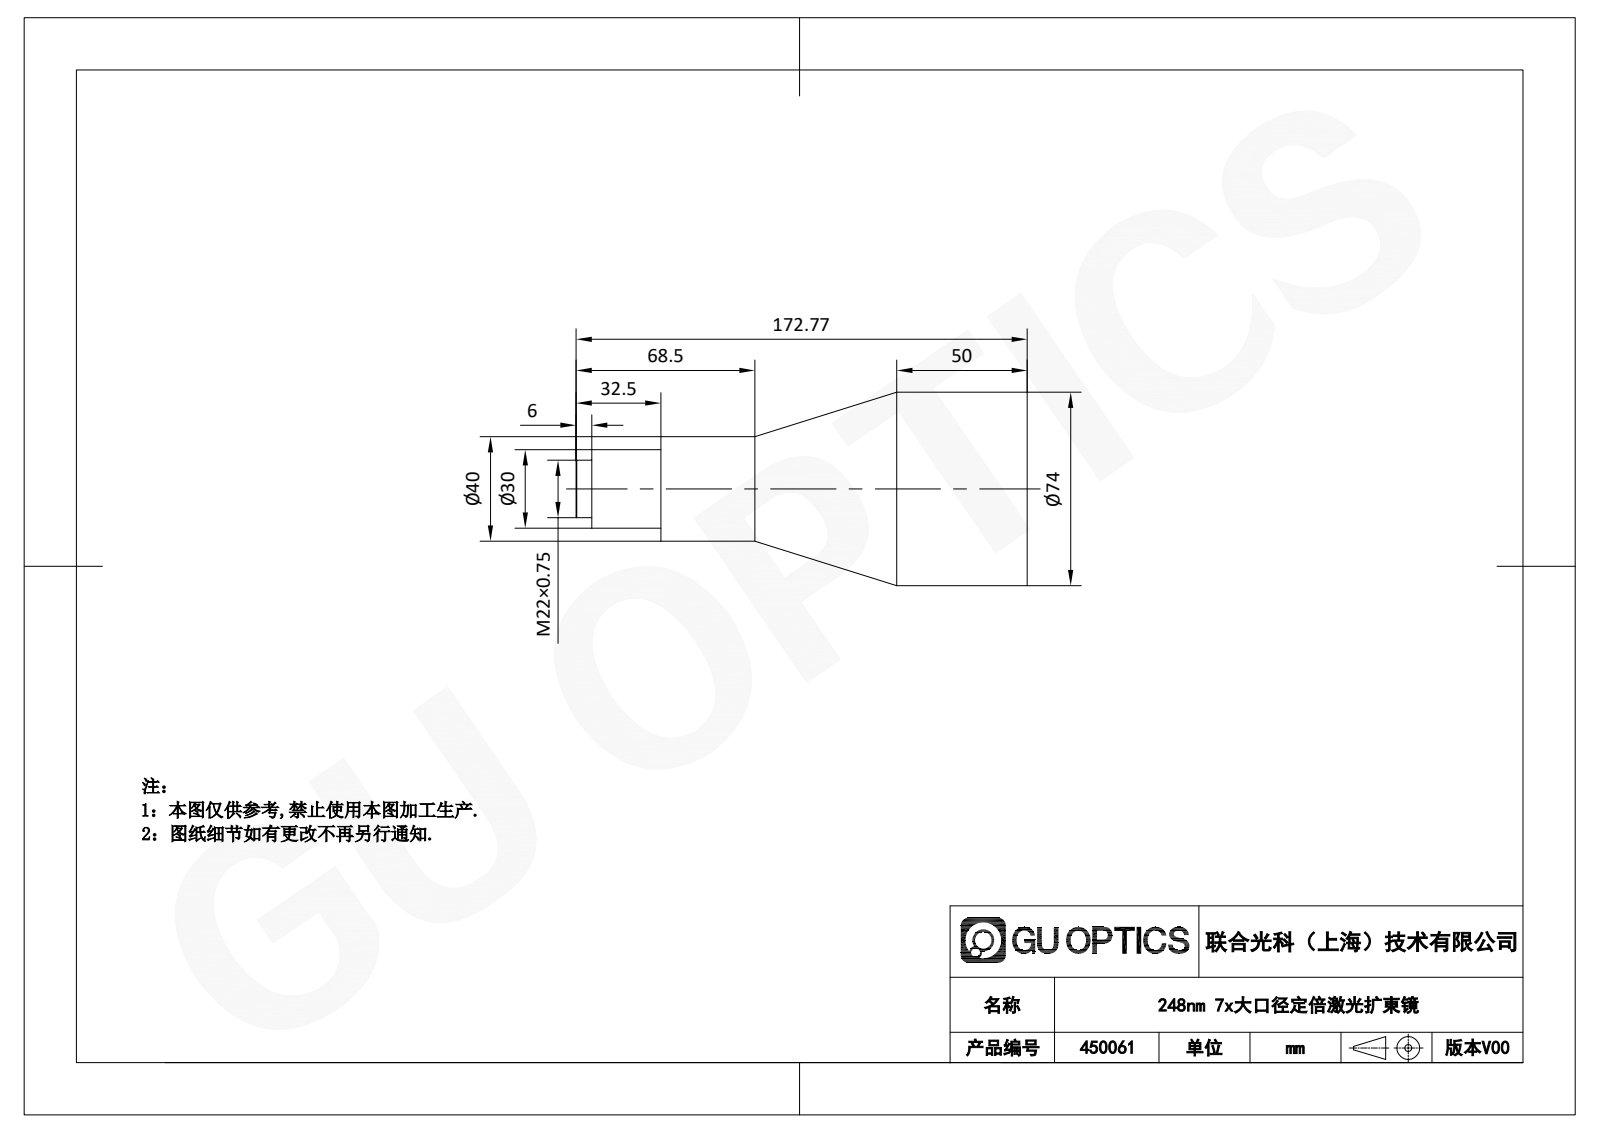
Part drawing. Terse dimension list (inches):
name: 450061
written by: SolidWorks 2020 (AUTOMOTIVE_DESIGN)
unit: in
bodies: 1 solid, 16 faces (4 planar, 8 cylindrical, 4 other)
size: 6.802 × 2.913 × 2.913
volume: 25.87 in³; area: 53.93 in²
bosses: 1× ⌀2.913, 1× ⌀1.575, 1× ⌀1.181, 1× ⌀0.866
face distances: 5.522, 1.28, 6.802, 0.236, 1.043, 6.566
